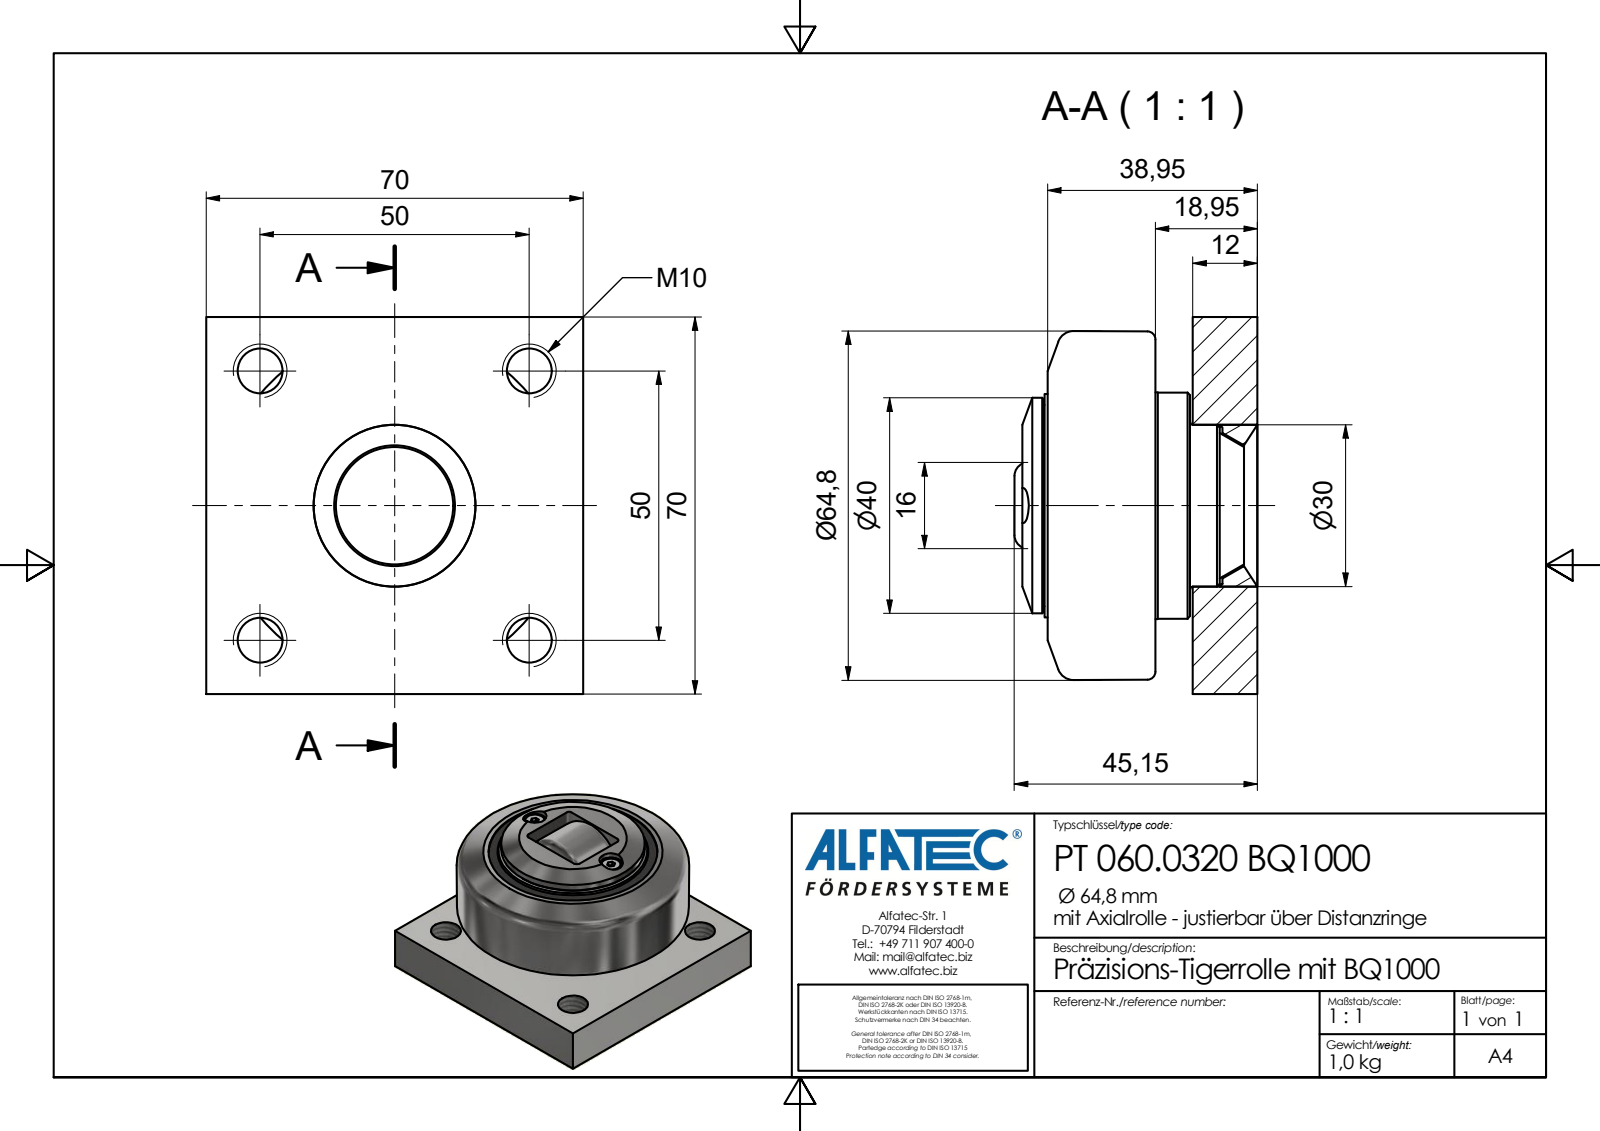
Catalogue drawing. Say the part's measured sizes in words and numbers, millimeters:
The part is named "PT 060.0320 BQ1000_Kontur". Its 3-D file was written by "Autodesk Inventor 2020 (AP242_MANAGED_MODEL_BASED_3D_ENGINEERING_MIM_LF)". It is 1 solid with 119 faces: 51 planar, 40 cylindrical and 28 other. Overall it measures 70 by 70 by 45.15 millimeters. Its volume is 130 068 cubic millimeters and its surface area 29 396 square millimeters. Round holes: 4 of diameter 8.38, 2 of diameter 3.4, 2 of diameter 6.5, 1 of diameter 10.2, 1 of diameter 13, 1 of diameter 16, 1 of diameter 38, 1 of diameter 42, 1 of diameter 42.97, 1 of diameter 47. Round bosses or shafts: 2 of diameter 5.35, 2 of diameter 3, 1 of diameter 42.1, 1 of diameter 41.5, 1 of diameter 40, 1 of diameter 25, 1 of diameter 11. Partial cylindrical surfaces (rounded edges, fillets, slot ends): 4 of radius 1, 1 of radius 12.47. The main face-to-face distances are 12, 70, 18.95, 6.95, 20.7, 39.65, 27.65, 20, 0.45, 0.7. The hole center spacings are 26.93, 35.36, 47.17, 50, 15, 30, 70.71, 26.91.
